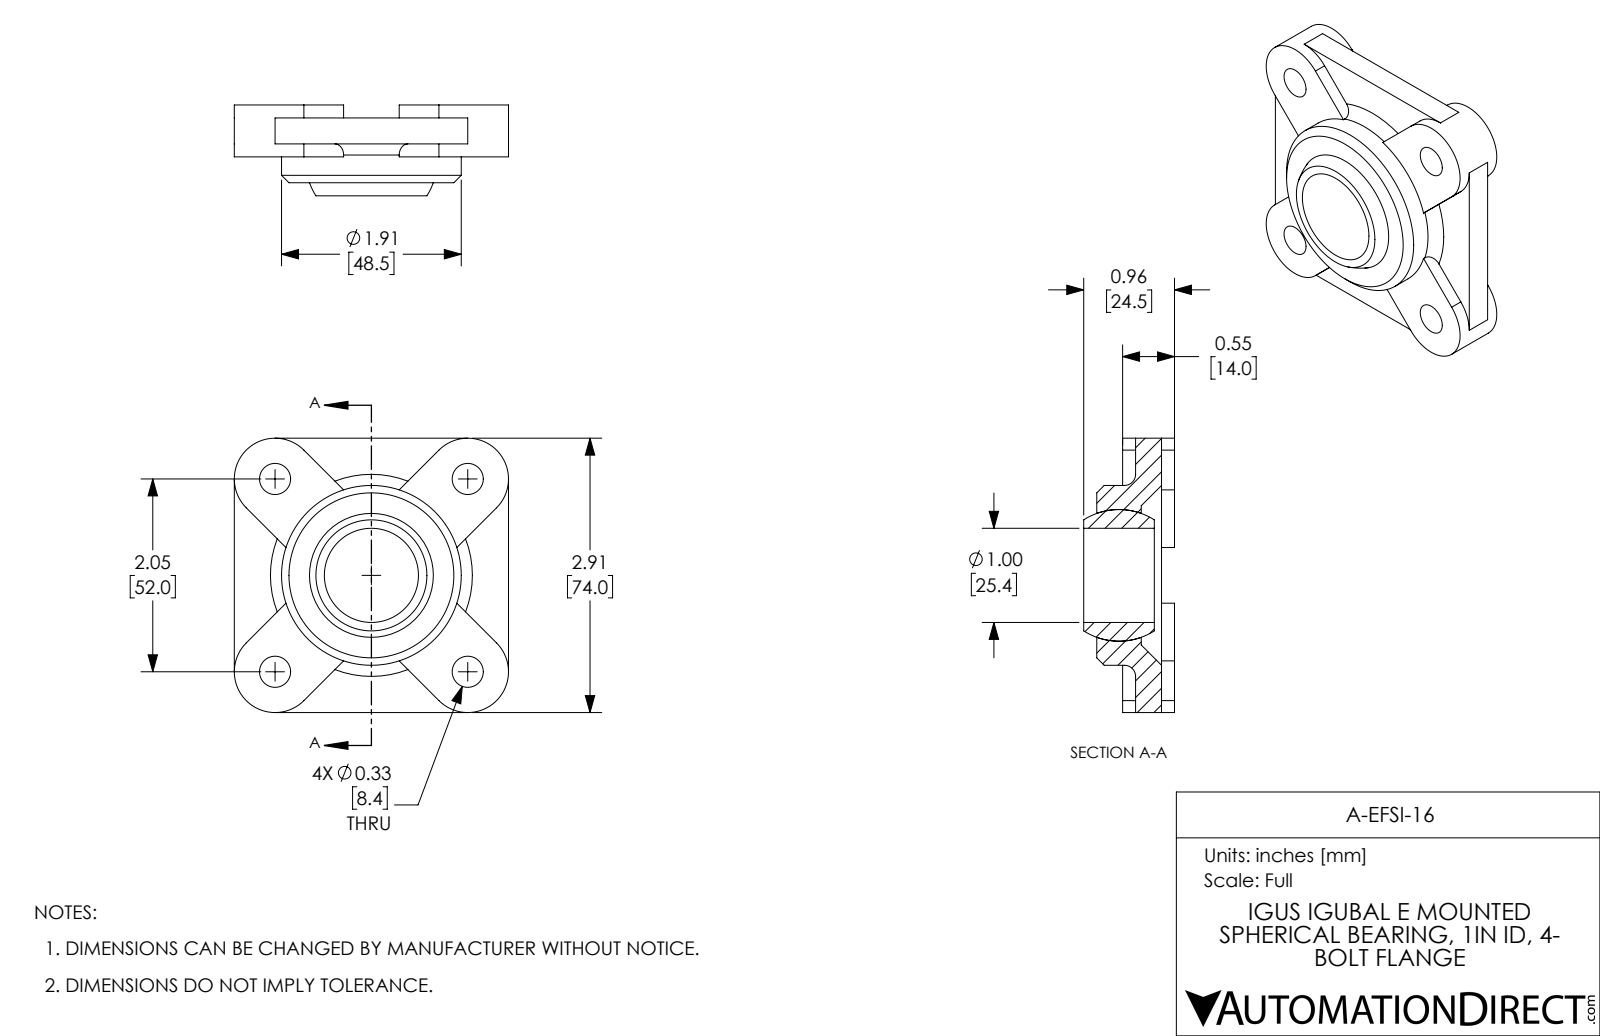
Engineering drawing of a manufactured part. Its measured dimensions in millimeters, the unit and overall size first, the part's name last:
Units: millimetres
Overall size (bounding box): 74 × 74 × 32.7
Round holes (diameter × count): ⌀8.4 ×4, ⌀25.4 ×1, ⌀48.5 ×1
Partial cylindrical surfaces — rounded edges, fillets, slot ends (radius × count): R11 ×4
Main face-to-face distances: 10.5, 3.5, 14, 7, 74, 21, 17.5, 10.5, 7, 22
Hole centre spacings: 36.8, 52, 73.5
Volume: 55 190 mm³ · Surface area: 20 790 mm²
Bodies: 2 solids, 77 faces (40 planar, 24 cylindrical, 13 other)
Part name (STEP PRODUCT): A-EFSI-16
STEP written by: SolidWorks 2017 (AUTOMOTIVE_DESIGN)
